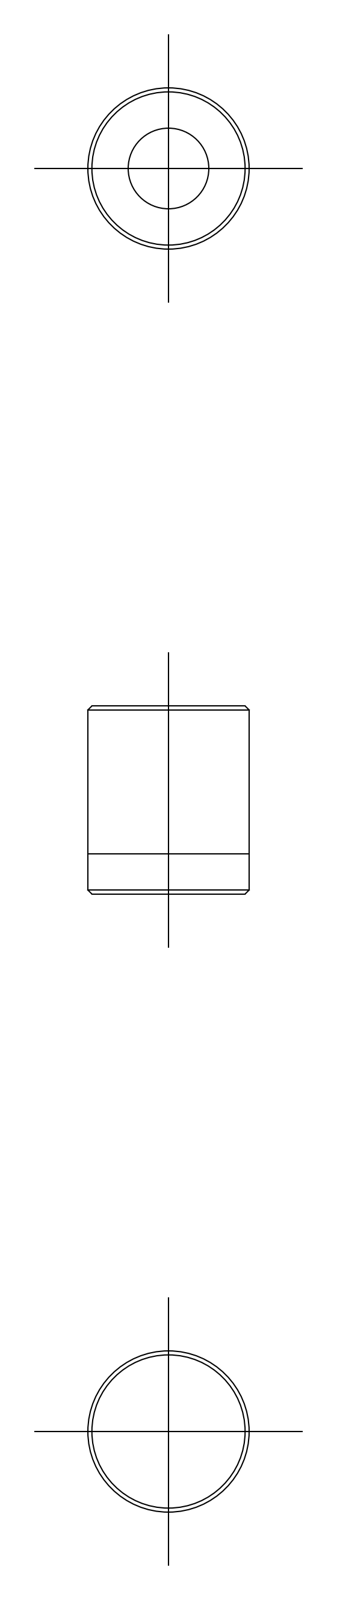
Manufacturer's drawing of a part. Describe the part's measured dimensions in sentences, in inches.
Its 3-D file was written by "CADfix (AUTOMOTIVE_DESIGN)". It is 1 solid with 16 faces: 0 planar, 0 cylindrical and 16 other. Overall it measures 0.551 by 0.472 by 0.472 inches. Its volume is 0.095 cubic inches and its surface area 1.2 square inches.
